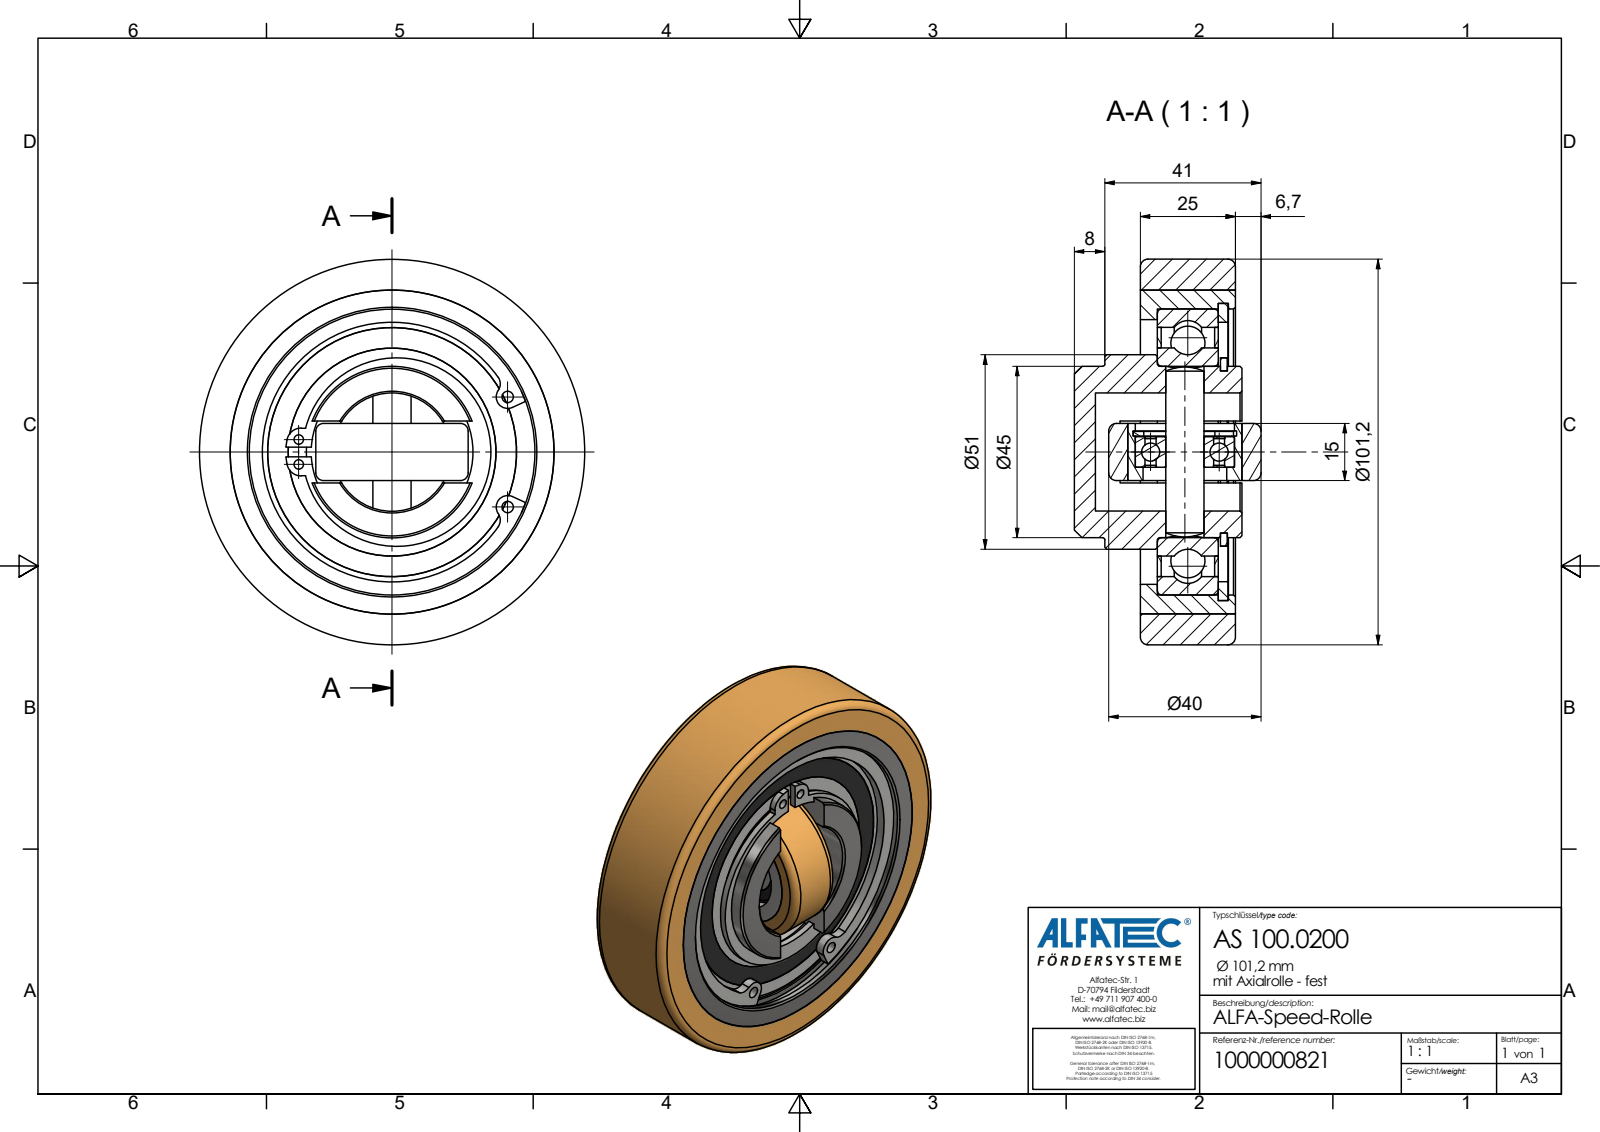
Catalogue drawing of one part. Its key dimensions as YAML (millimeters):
part_name: "AS 100.0200_Kontur"
step_written_by: "Autodesk Inventor 2020 (AP242_MANAGED_MODEL_BASED_3D_ENGINEERING_MIM_LF)"
units: millimeters
bodies: {solids: 1, faces: 47, planar: 22, cylindrical: 12, other: 13}
overall_size: [101.2, 101.2, 49]
volume: 222928
surface_area: 29122
round_holes:
  - {diameter: 31, count: 1}
round_bosses_or_shafts:
  - {diameter: 101.2, count: 1}
  - {diameter: 51, count: 1}
  - {diameter: 45, count: 1}
partial_cylinders:
  - {radius: 13, count: 1}
  - {radius: 13.6, count: 1}
  - {radius: 20, count: 1}
face_to_face_distances: [25, 17.3, 42.3, 44, 26.7, 1.7, 12, 5.3, 30.3, 32]
